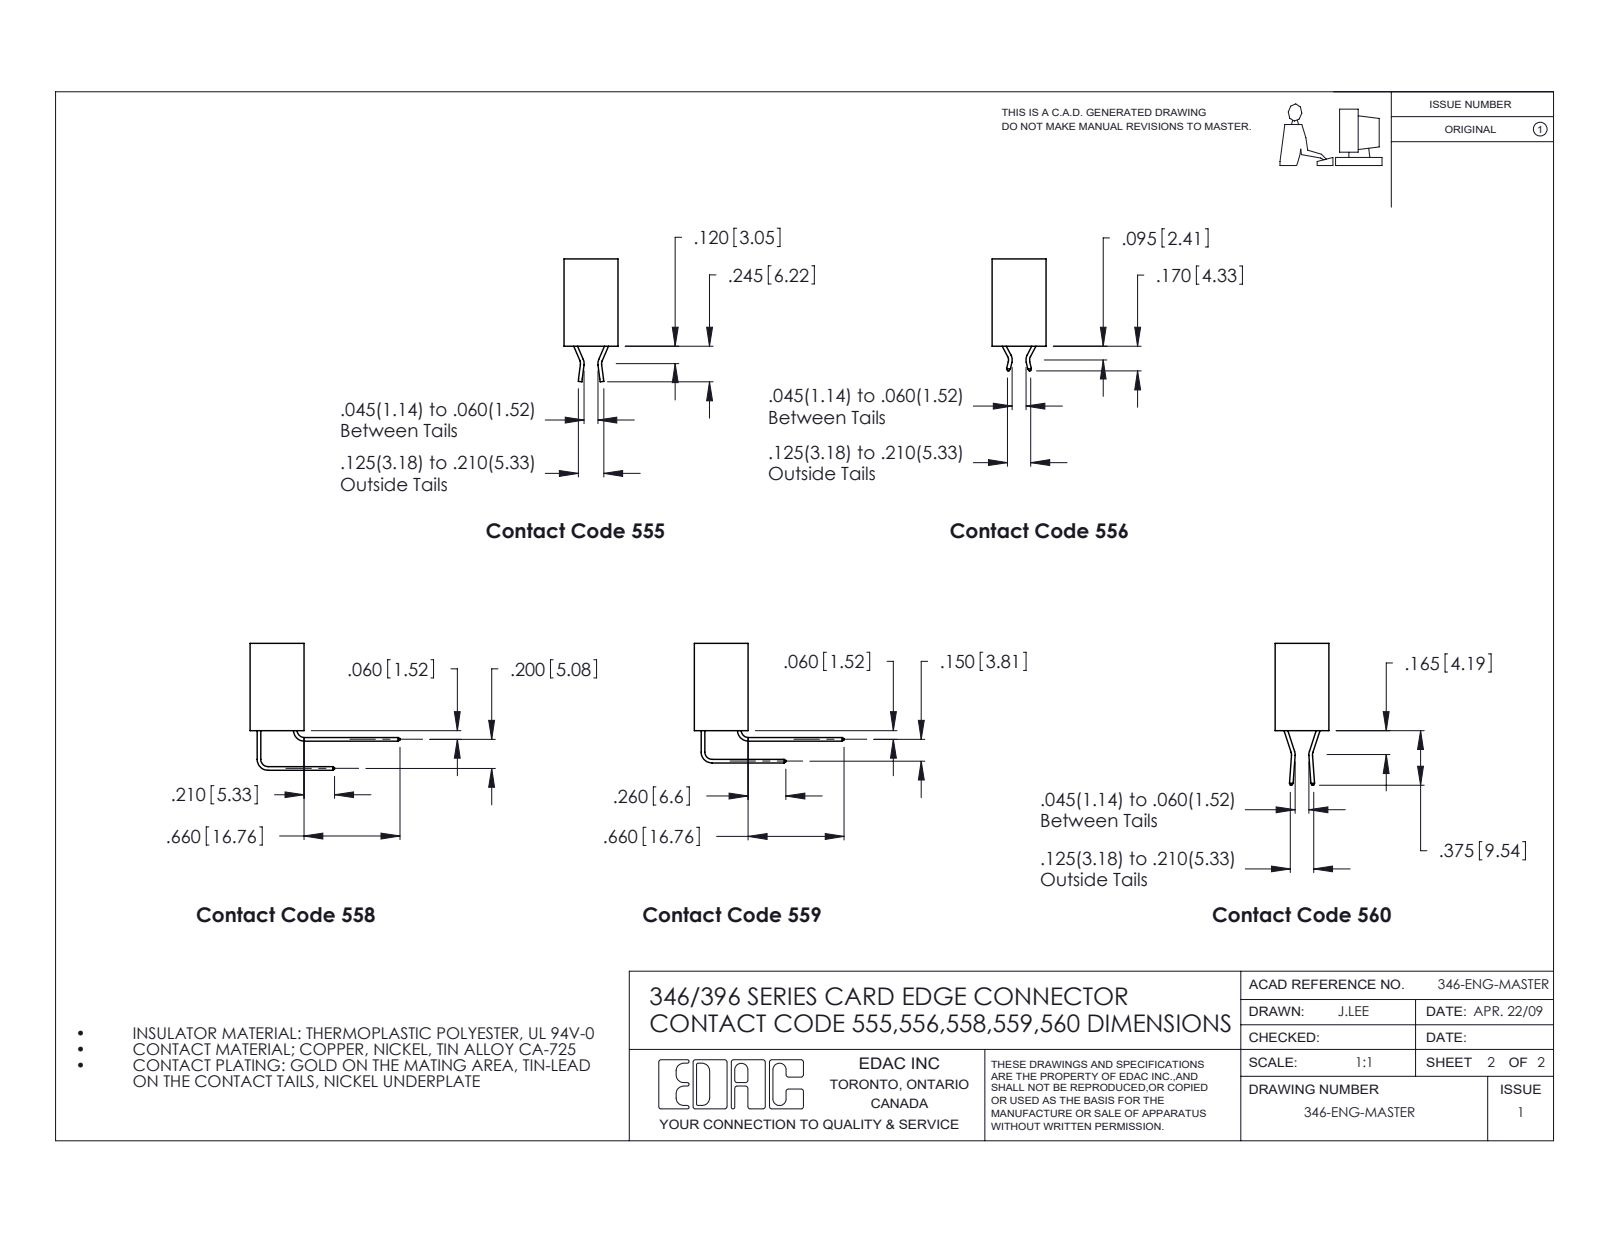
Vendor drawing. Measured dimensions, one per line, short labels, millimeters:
name: 345-292-001_345-293-141; 346 Part_0.170 Offset - 0.156 Dia-TH; 345-250-002_345-250-002-102; 346-005-541-603
written by: SolidWorks 2020 (CONFIG_CONTROL_DESIGN)
unit: mm
bodies: 8 solids, 468 faces (304 planar, 156 cylindrical, 8 other)
size: 36.4 × 34.3 × 9.4
volume: 3 100 mm³; area: 3 982 mm²
holes: 2× ⌀2.9, 2× ⌀4, 1× ⌀1.6
bosses: 2× ⌀6.4, 2× ⌀4.6, 2× ⌀3.5
rounds: 22× R0.3, 10× R0.2, 10× R0.3, 6× R0.2, 6× R0.8, 3× R0.7, 2× R0.8, 2× R1
face distances: 6.4, 9.4, 1.2, 8.2, 0.6, 1.8, 7.6, 5.6, 3.8, 2.5
hole spacings: 6.2, 24.6, 29.7
